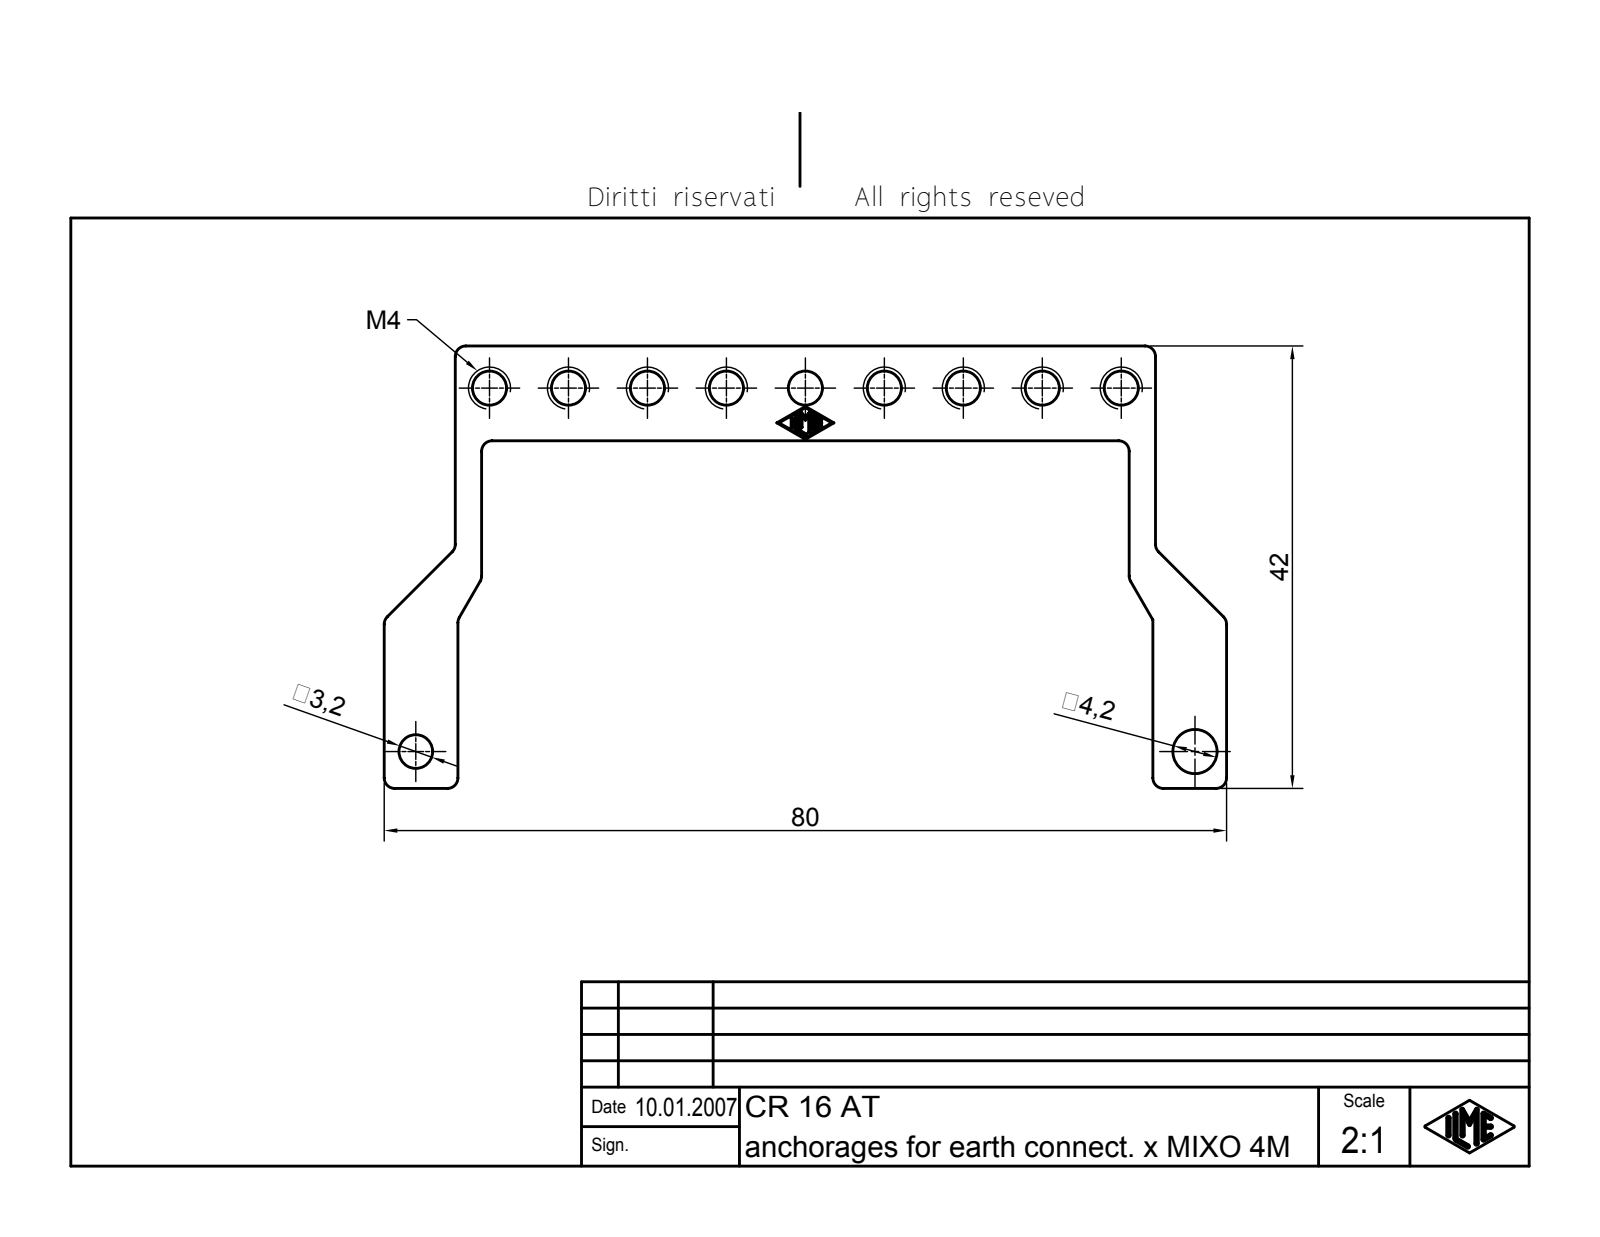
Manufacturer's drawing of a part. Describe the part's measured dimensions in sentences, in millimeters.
The part is named "CR 16 AT". Its 3-D file was written by "Autodesk Inventor 7 (AUTOMOTIVE_DESIGN)". It is 1 solid with 121 faces: 55 planar, 48 cylindrical and 18 other. Overall it measures 80 by 42 by 2 millimeters. Its volume is 1 694 cubic millimeters and its surface area 2 524 square millimeters. Round holes: 1 of diameter 3.2, 1 of diameter 4.2. Partial cylindrical surfaces (rounded edges, fillets, slot ends): 15 of radius 1, 14 of radius 0.1. The main face-to-face distances are 2, 9, 66.25, 6.75, 7, 73, 73.25, 2.5, 9.25, 70.75. The hole center spacings are 74.
